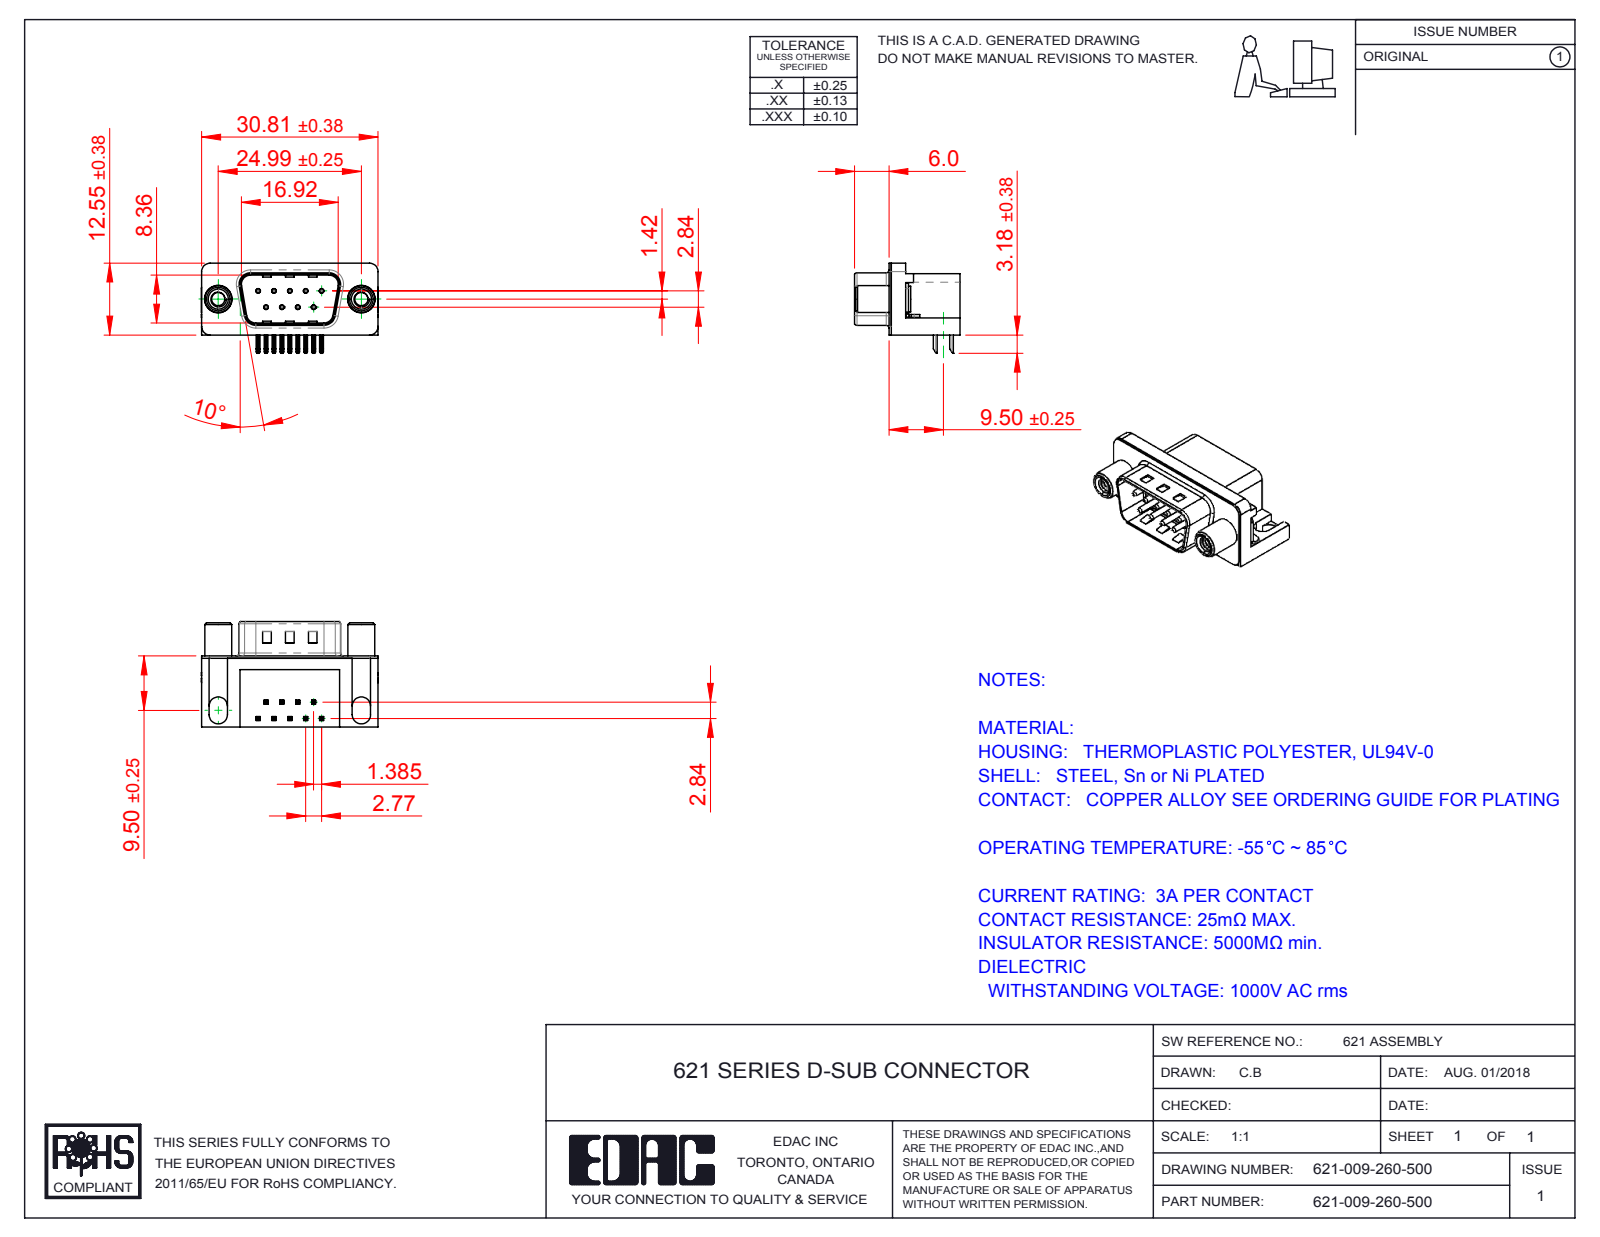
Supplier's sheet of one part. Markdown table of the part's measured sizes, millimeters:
| quantity | value |
| --- | --- |
| part name | 621 Contact Bottom; 621-009-260-500; 621 Shell_9 Socket; 621 Round Threaded Standoff (+3 more) |
| STEP written by | SolidWorks 2016 (CONFIG_CONTROL_DESIGN) |
| units | millimeters |
| bodies | 15 solids, 979 faces (563 planar, 319 cylindrical, 97 other) |
| overall size | 30.89 × 18.4 × 15.73 |
| volume | 3 300 mm³ |
| surface area | 4 447 mm² |
| round holes (diameter × count) | 0.35 × 9, 0.8 × 9, 2.3 × 2, 3.1 × 2, 4 × 2, 4.8 × 2, 5 × 2 |
| round bosses / shafts (diameter × count) | 0.75 × 9, 4.9 × 2, 4.7 × 2, 4.5 × 2, 3.85 × 2 |
| partial cylindrical surfaces (radius × count) | 0.25 × 36, 0.12 × 18, 1 × 16, 0.5 × 9, 1.5 × 8, 1.6 × 8, 0.9 × 4, 2 × 4 |
| main face-to-face distances | 0.4, 12, 12.4, 10.35, 2.9, 9.5, 2.5, 2.1, 0.35, 10.7 |
| hole center spacings | 3.16, 2.77, 5.54, 5.03, 5.04, 8.31, 7.48, 7.49 |
